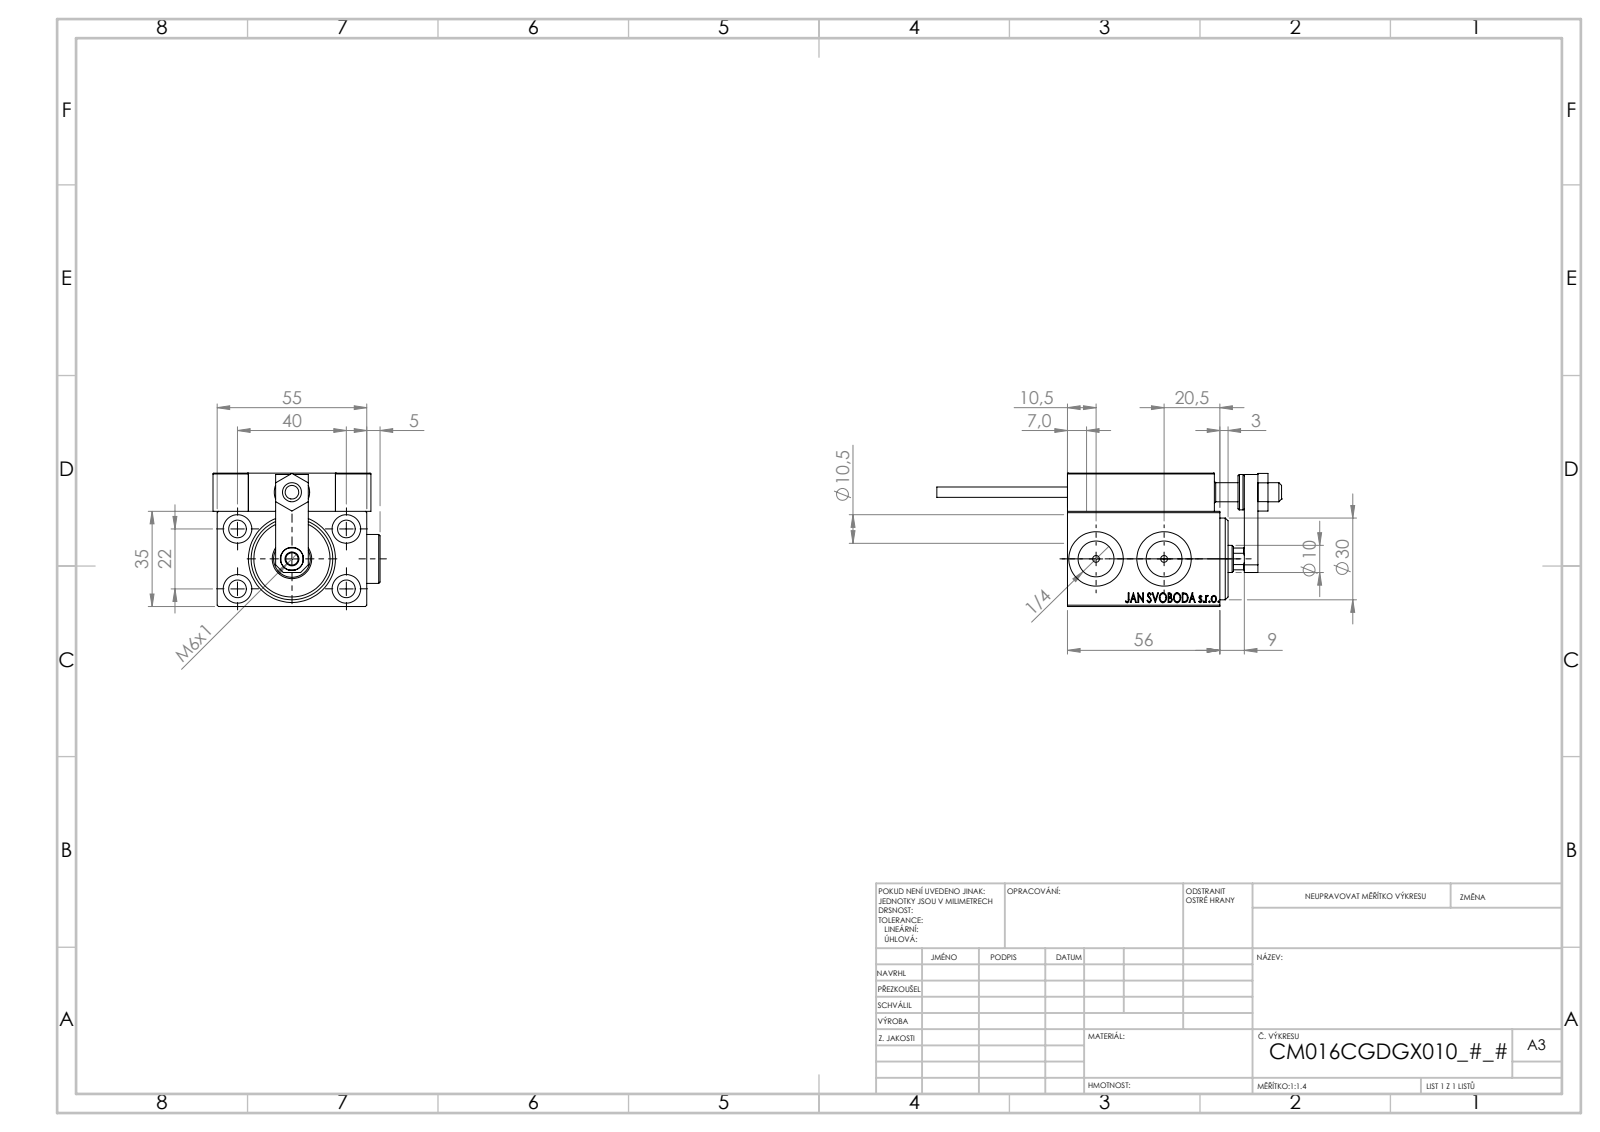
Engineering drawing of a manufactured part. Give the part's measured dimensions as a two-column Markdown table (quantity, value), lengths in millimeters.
| quantity | value |
| --- | --- |
| part name | SWITCH X; SWITCH DIM B,W; MAGNET; SWITCH_X_FRONT_BACK (+8 more) |
| STEP written by | SolidWorks 2019 (CONFIG_CONTROL_DESIGN) |
| units | millimeters |
| bodies | 25 solids, 1339 faces (595 planar, 206 cylindrical, 538 other) |
| overall size | 126.7 × 61.4 × 49 |
| volume | 134 628 mm³ |
| surface area | 52 697 mm² |
| round holes (diameter × count) | 8 × 5, 3.2 × 4, 4 × 4, 6.5 × 4, 10.5 × 4, 2.5 × 2, 5 × 2, 13.16 × 2, 20 × 2, 4.5 × 1, 7 × 1, 8.5 × 1 |
| round bosses / shafts (diameter × count) | 18 × 2, 5 × 2, 3.8 × 2, 13 × 1, 11 × 1 |
| partial cylindrical surfaces (radius × count) | 0.3 × 26, 3 × 2, 4.5 × 1 |
| main face-to-face distances | 49, 35, 5, 14, 3, 7, 10, 1.5, 44, 55 |
| hole center spacings | 22.83, 8.25, 11.37, 20, 22, 23.41, 24.13, 29.59 |
